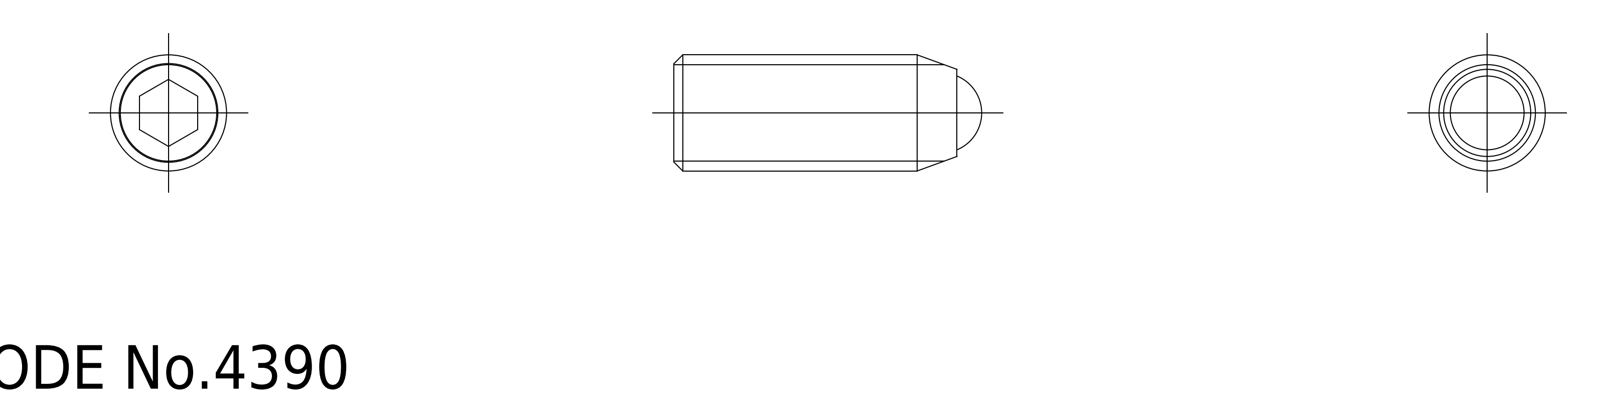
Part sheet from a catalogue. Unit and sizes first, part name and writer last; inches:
Units: inches
Overall size (bounding box): 0.835 × 0.315 × 0.315
Volume: 0.051 in³ · Surface area: 1.26 in²
Bodies: 2 solids, 20 faces (0 planar, 0 cylindrical, 20 other)
Part name (STEP PRODUCT): ball; SCS_M8_20_R_17848_36
STEP written by: CADfix (AUTOMOTIVE_DESIGN)
